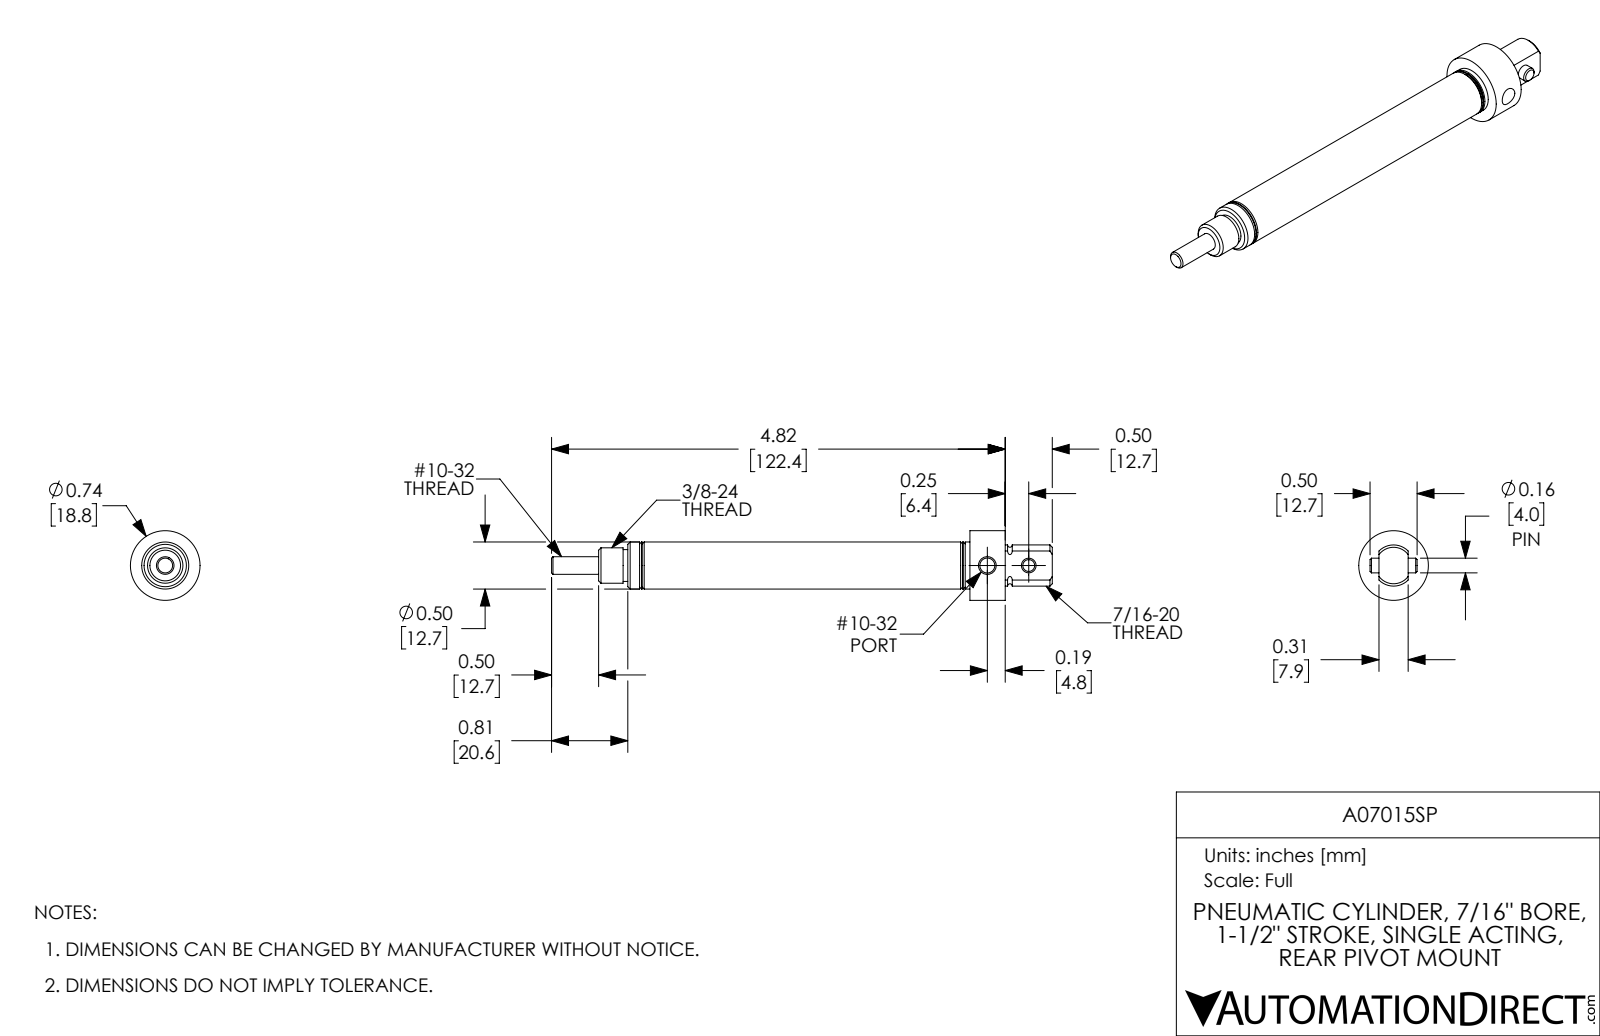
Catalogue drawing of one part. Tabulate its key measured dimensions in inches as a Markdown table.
| quantity | value |
| --- | --- |
| part name | A07015SP-MainBody; A07015SP-Pin; A07015SP; A07015SP-Rod |
| STEP written by | SolidWorks 2017 (AUTOMOTIVE_DESIGN) |
| units | inches |
| bodies | 3 solids, 82 faces (20 planar, 36 cylindrical, 26 other) |
| overall size | 5.32 × 0.74 × 0.74 |
| volume | 0.787 in³ |
| surface area | 15.99 in² |
| round holes (diameter × count) | 0.156 × 1, 0.159 × 1, 0.187 × 1, 0.19 × 1 |
| round bosses / shafts (diameter × count) | 0.74 × 1, 0.5 × 1, 0.437 × 1, 0.376 × 1, 0.338 × 1 |
| main face-to-face distances | 1.005, 0.5, 0.375, 0.63, 1.505, 3.005, 0.31, 1.13, 2.63, 2 |
| hole center spacings | 0.44 |
